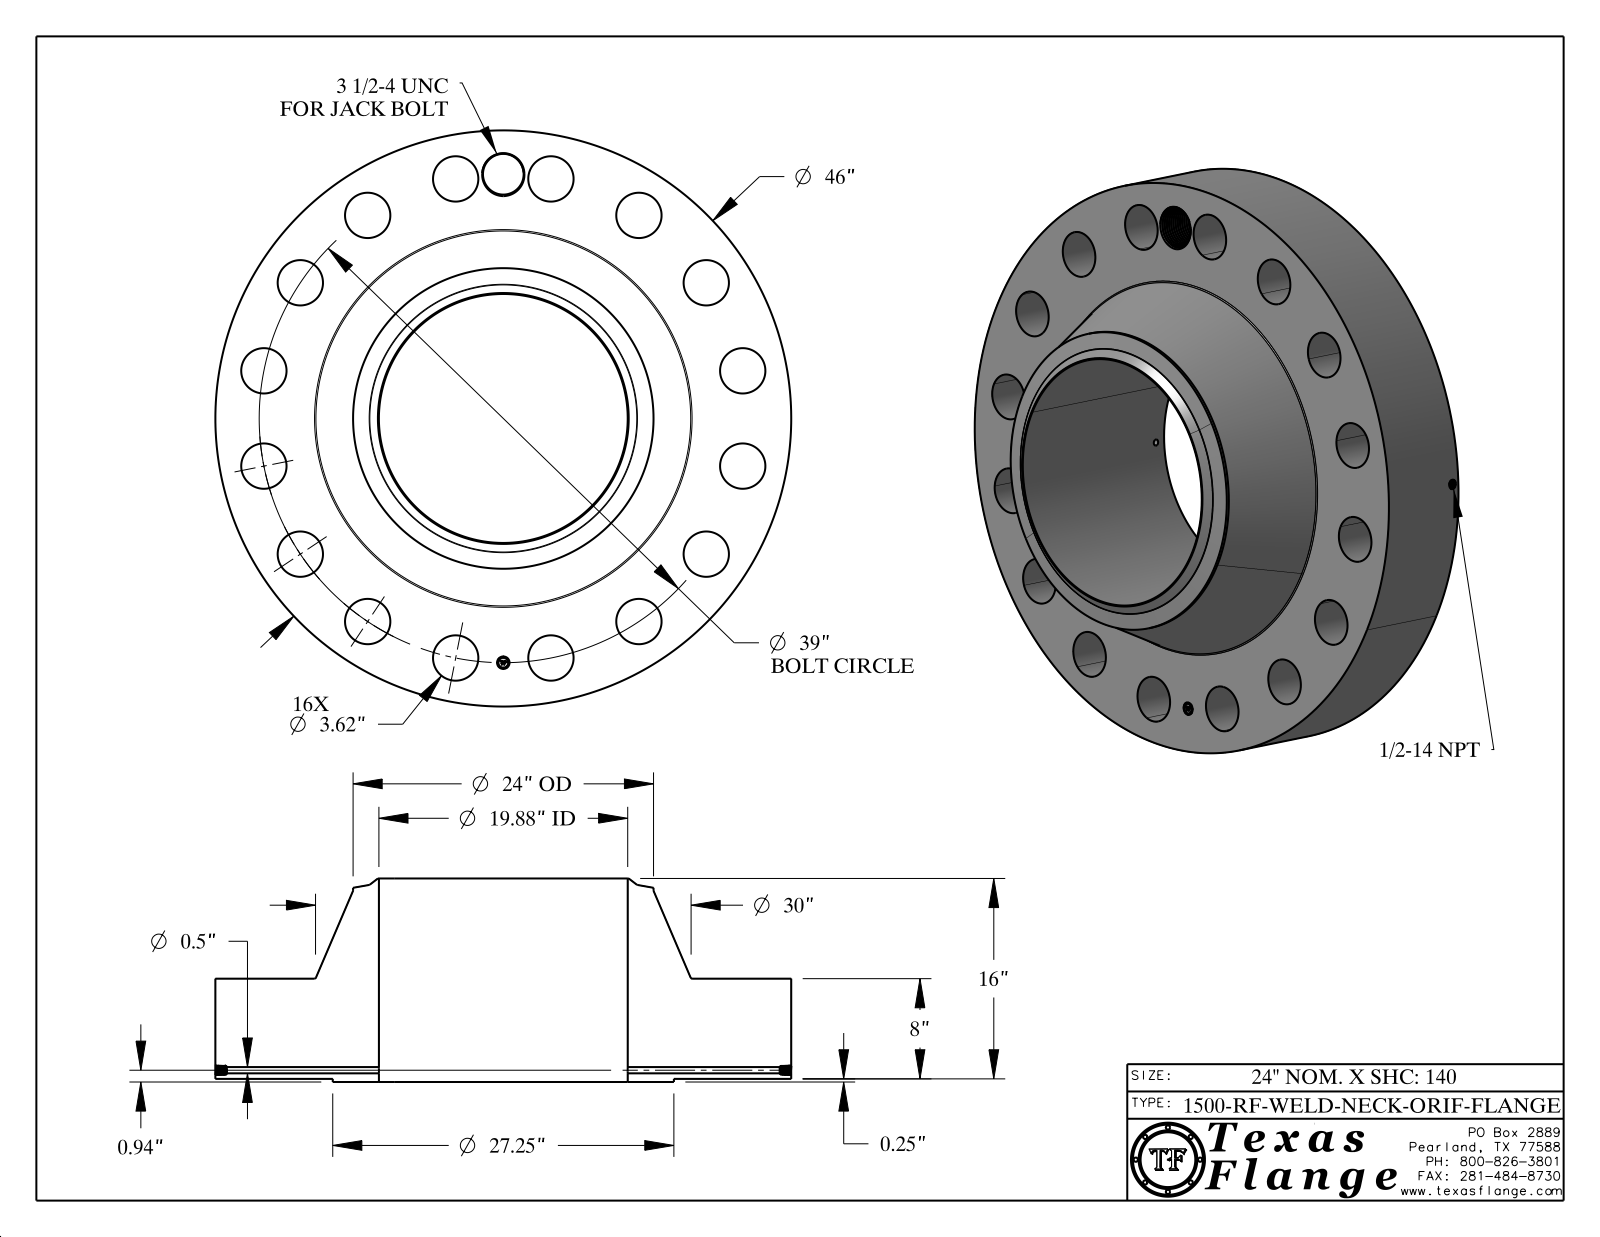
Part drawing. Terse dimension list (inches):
name: 1500-RF-WELD-NECK
written by: CATIA V5 STEP AP214 (AUTOMOTIVE_DESIGN)
unit: in
bodies: 1 solid, 891 faces (369 planar, 144 cylindrical, 378 other)
size: 46 × 46 × 16.25
volume: 11 413 in³; area: 6 590 in²
holes: 16× ⌀3.62, 1× ⌀0.5, 1× ⌀0.672, 1× ⌀1, 1× ⌀3.25, 1× ⌀19.876
bosses: 8× ⌀0.061, 1× ⌀46, 1× ⌀27.25, 1× ⌀24, 1× ⌀0.788
face distances: 8, 0.25, 8.25, 16.25, 16, 8.235, 7.985, 0.015, 8.015, 0.298
hole spacings: 19.5, 27.577, 36.031, 32.427, 7.608, 14.924, 14.925, 21.667
